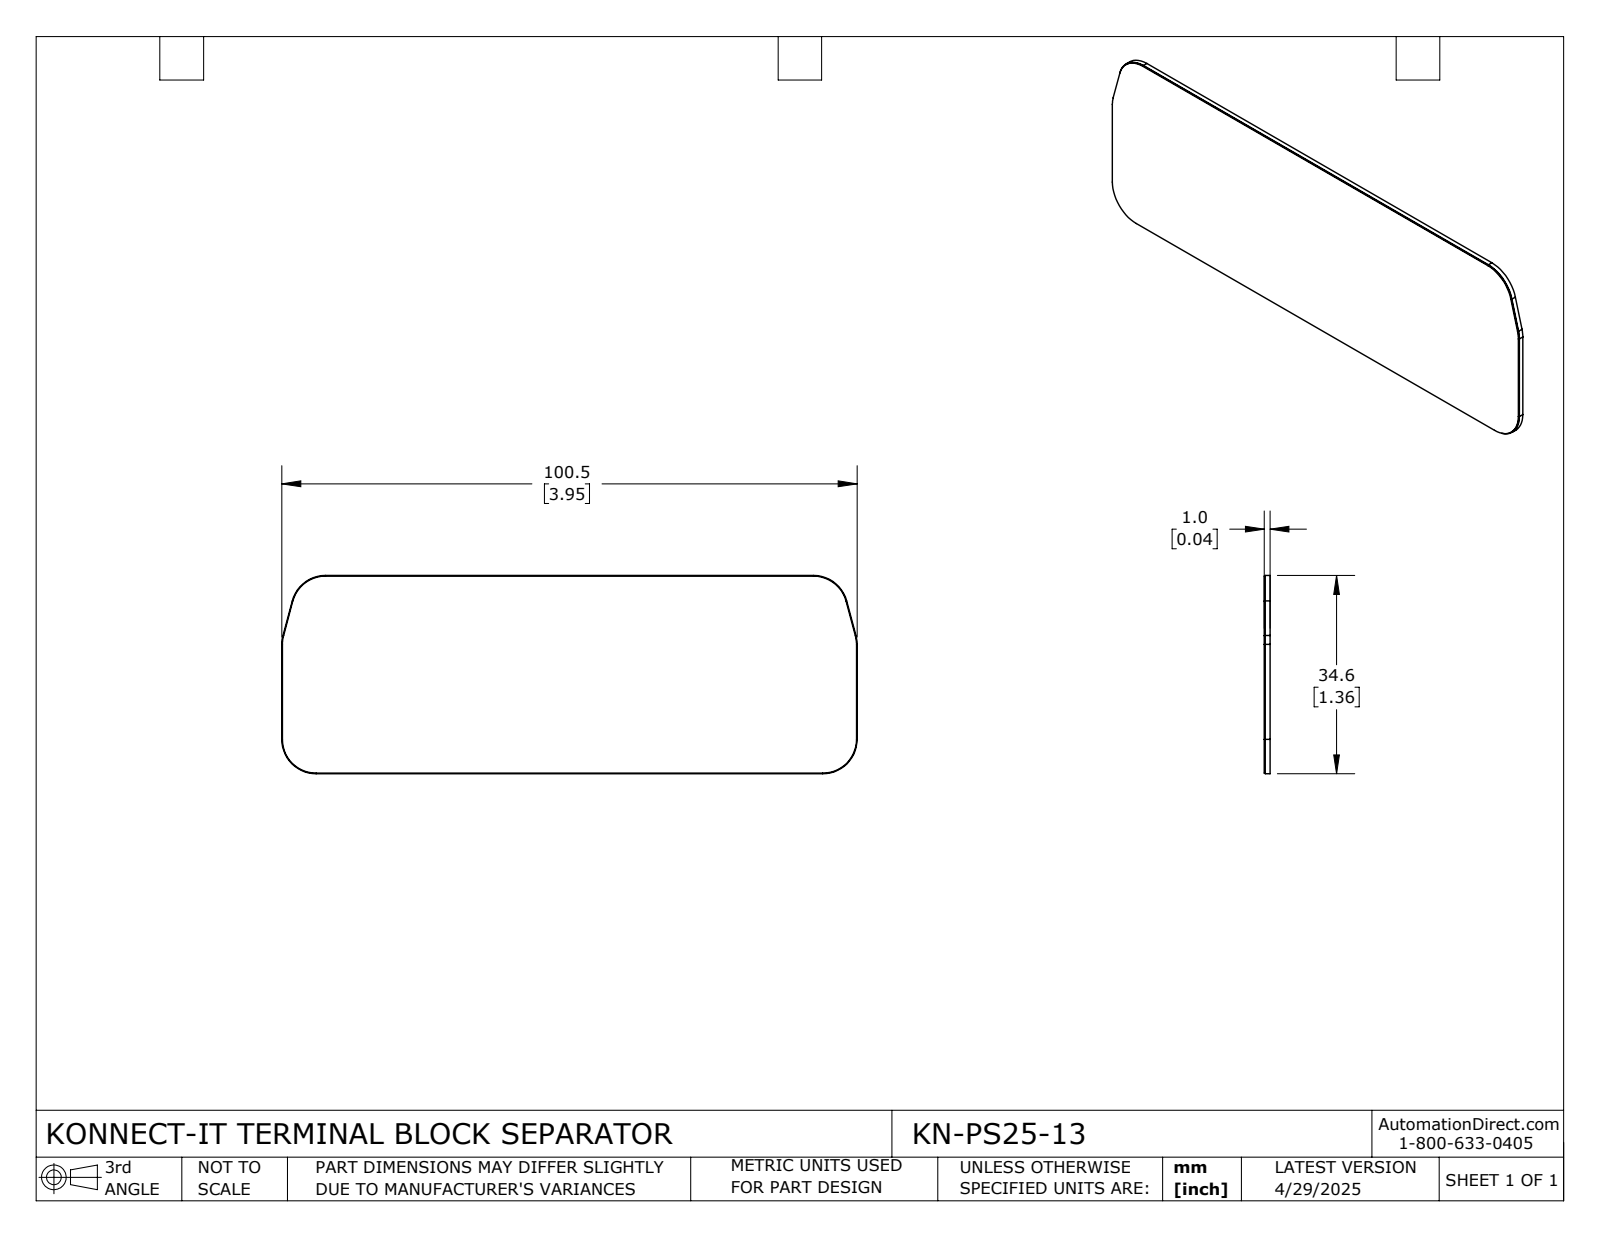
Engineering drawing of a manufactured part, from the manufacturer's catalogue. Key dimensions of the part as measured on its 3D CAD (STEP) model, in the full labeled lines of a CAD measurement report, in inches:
Part name (STEP PRODUCT): KN-PS25-13
STEP written by: SolidWorks 2024 (CONFIG_CONTROL_DESIGN)
Units: inches
Bodies: 1 solid, 27 faces (15 planar, 12 cylindrical, 0 other)
Overall size (bounding box): 3.955 × 1.363 × 0.039
Volume: 0.208 in³ · Surface area: 11 in²
Partial cylindrical surfaces — rounded edges, fillets, slot ends (radius × count): R0.232 ×6, R0.236 ×6
Main face-to-face distances: 0.039, 1.363, 1.359, 0.033, 3.955, 1.355, 3.951, 3.947
